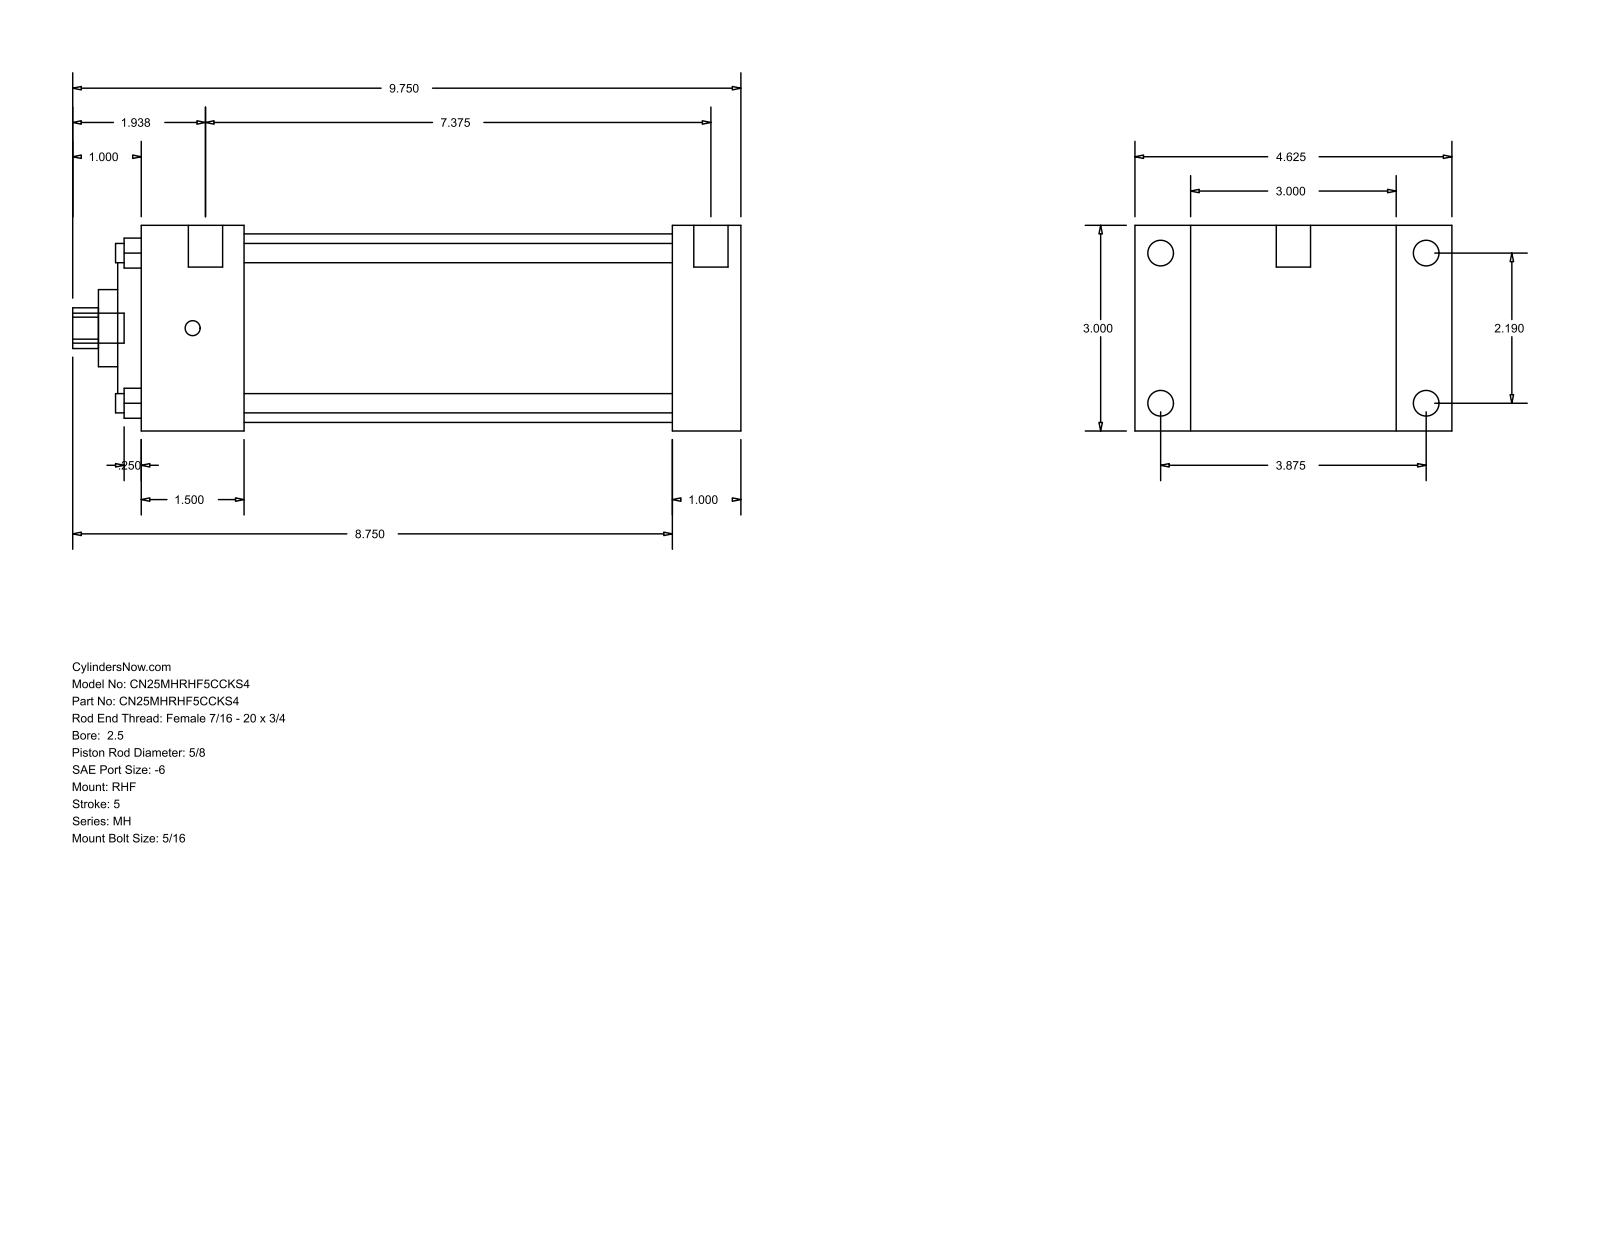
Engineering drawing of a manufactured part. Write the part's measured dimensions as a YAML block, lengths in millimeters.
part_name: "MH_RHF__0250_0.625"
step_written_by: "GSSL Pune (CONFIG_CONTROL_DESIGN)"
units: millimeters
bodies: {solids: 0, faces: 90, planar: 61, cylindrical: 29, other: 0}
overall_size: [247.65, 117.47, 76.2]
round_holes:
  - {diameter: 7.14, count: 4}
  - {diameter: 15.88, count: 1}
  - {diameter: 28.57, count: 1}
  - {diameter: 55.55, count: 1}
  - {diameter: 69.85, count: 1}
round_bosses_or_shafts:
  - {diameter: 9.53, count: 4}
  - {diameter: 5.56, count: 4}
  - {diameter: 12.7, count: 2}
  - {diameter: 11.11, count: 1}
partial_cylinders:
  - {radius: 7.54, count: 1}
face_to_face_distances: [76.2, 25.4, 20.64, 96.84, 222.25, 196.85, 117.48, 38.1, 158.75, 184.15]
hole_center_spacings: [39.33, 55.62, 78.66]
